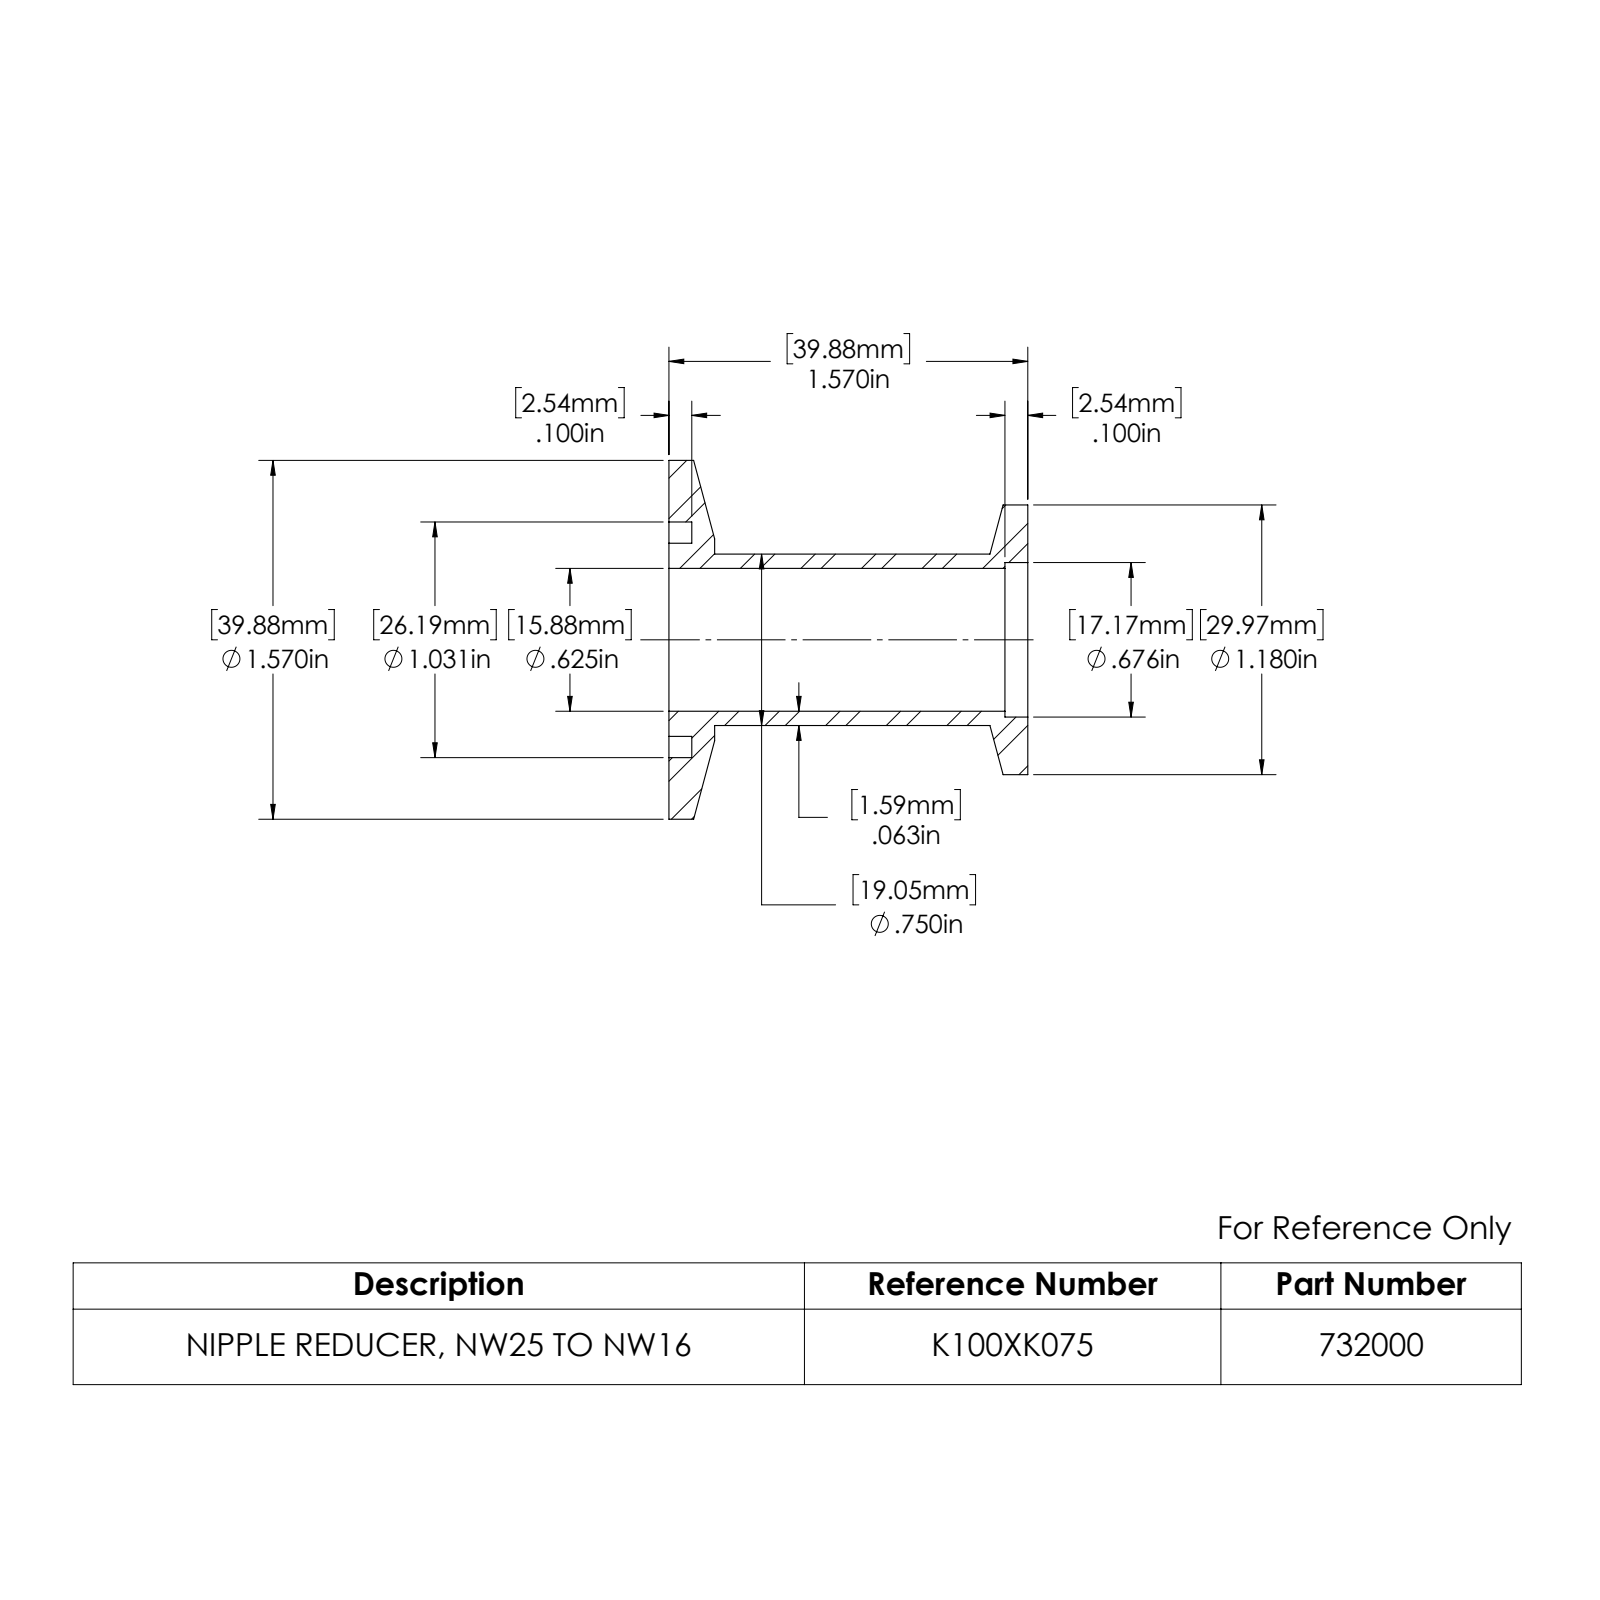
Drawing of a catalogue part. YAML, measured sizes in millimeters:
part_name: "732000"
step_written_by: "SolidWorks 2022 (AUTOMOTIVE_DESIGN)"
units: millimeters
bodies: {solids: 1, faces: 24, planar: 6, cylindrical: 14, other: 4}
overall_size: [39.9, 39.9, 39.9]
volume: 8180
surface_area: 7800
round_holes:
  - {diameter: 15.9, count: 1}
  - {diameter: 17.2, count: 1}
  - {diameter: 26.2, count: 1}
round_bosses_or_shafts:
  - {diameter: 39.9, count: 1}
  - {diameter: 30, count: 1}
  - {diameter: 21.5, count: 1}
  - {diameter: 19.1, count: 1}
face_to_face_distances: [39.9, 2.5, 37.3, 34.8, 5.1, 32.3]
